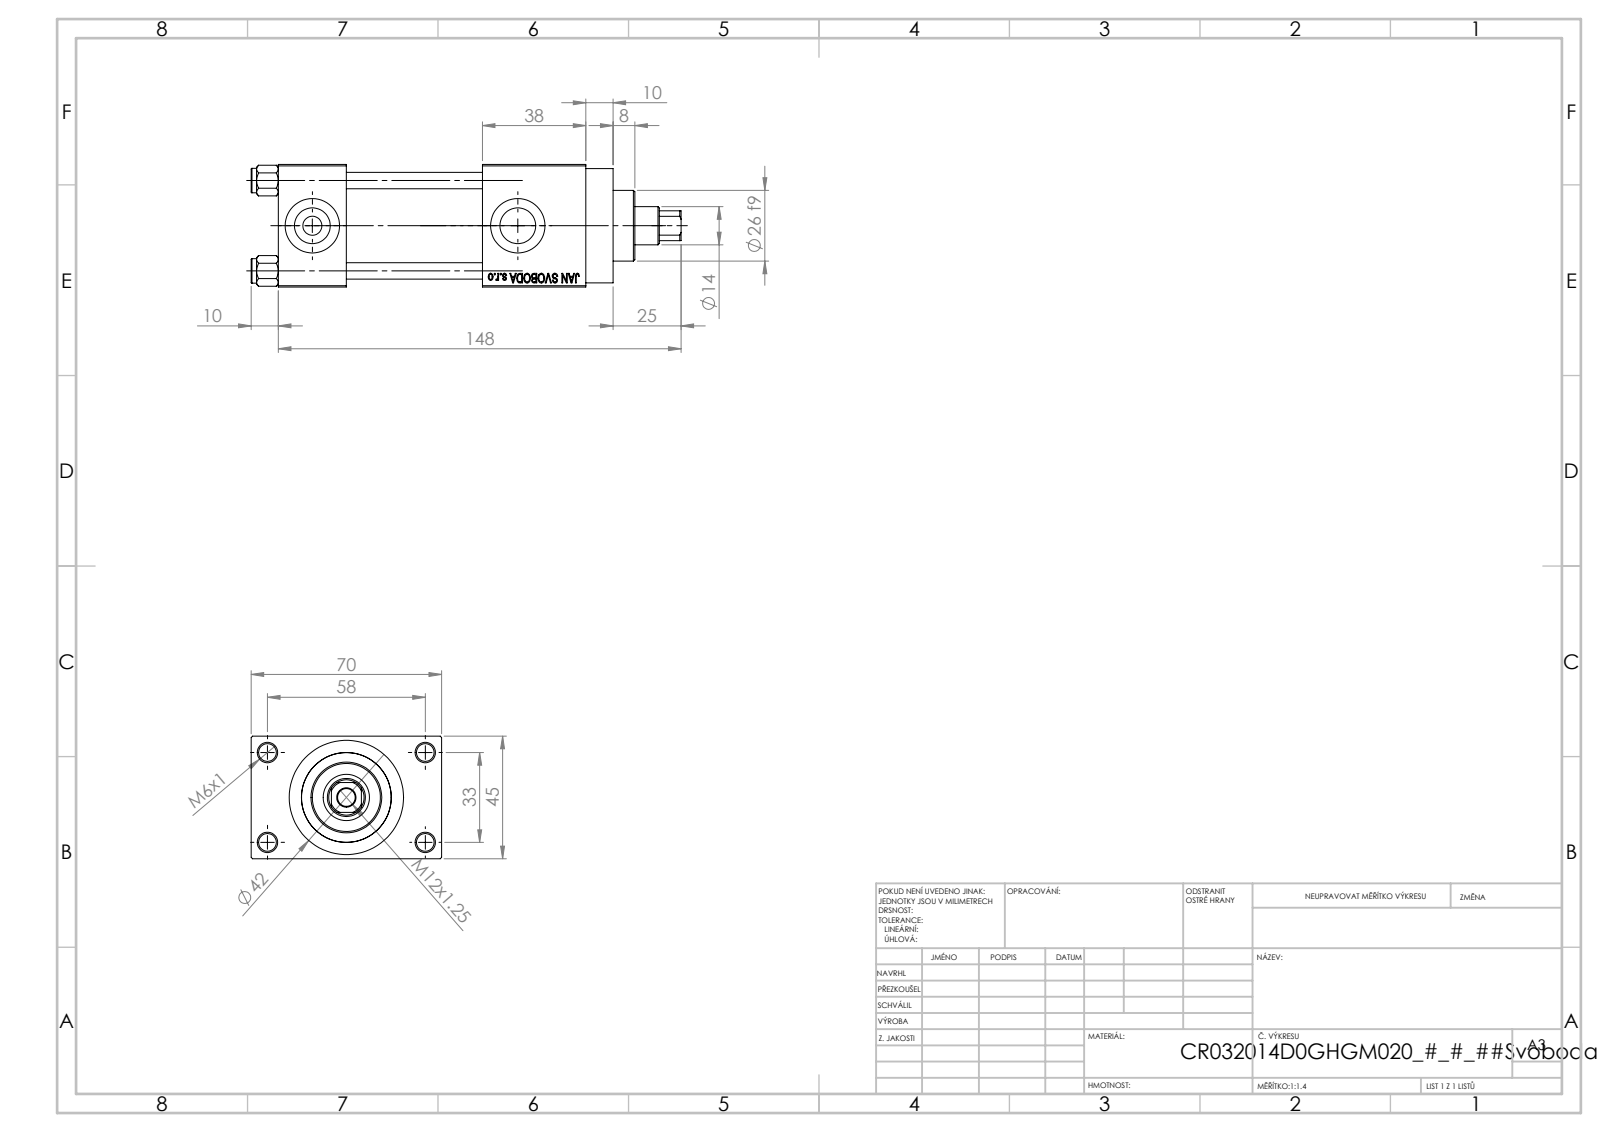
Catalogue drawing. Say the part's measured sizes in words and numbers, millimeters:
The part is named "V215CR_D_TYCINKA; V215CR_VCP_D; NUT_M5_D; V215CR_D_Body (+1 more)". Its 3-D file was written by "SolidWorks 2019 (CONFIG_CONTROL_DESIGN)". It is 11 solids with 1102 faces: 496 planar, 88 cylindrical and 518 other. Overall it measures 158 by 70 by 45 millimeters. Its volume is 230 327 cubic millimeters and its surface area 75 388 square millimeters. Round holes: 5 of diameter 6.5, 4 of diameter 6, 2 of diameter 7, 2 of diameter 13.16, 2 of diameter 20, 1 of diameter 14, 1 of diameter 17, 1 of diameter 24, 1 of diameter 32, 1 of diameter 33. Round bosses or shafts: 4 of diameter 9, 1 of diameter 42, 1 of diameter 38, 1 of diameter 26. Partial cylindrical surfaces (rounded edges, fillets, slot ends): 1 of radius 6.5. The main face-to-face distances are 45, 25, 50, 12.5, 75, 57.5, 88, 38, 113, 70. The hole center spacings are 12.4, 23.48, 33.2, 33.37, 35.35, 45.6, 56.35, 33.
